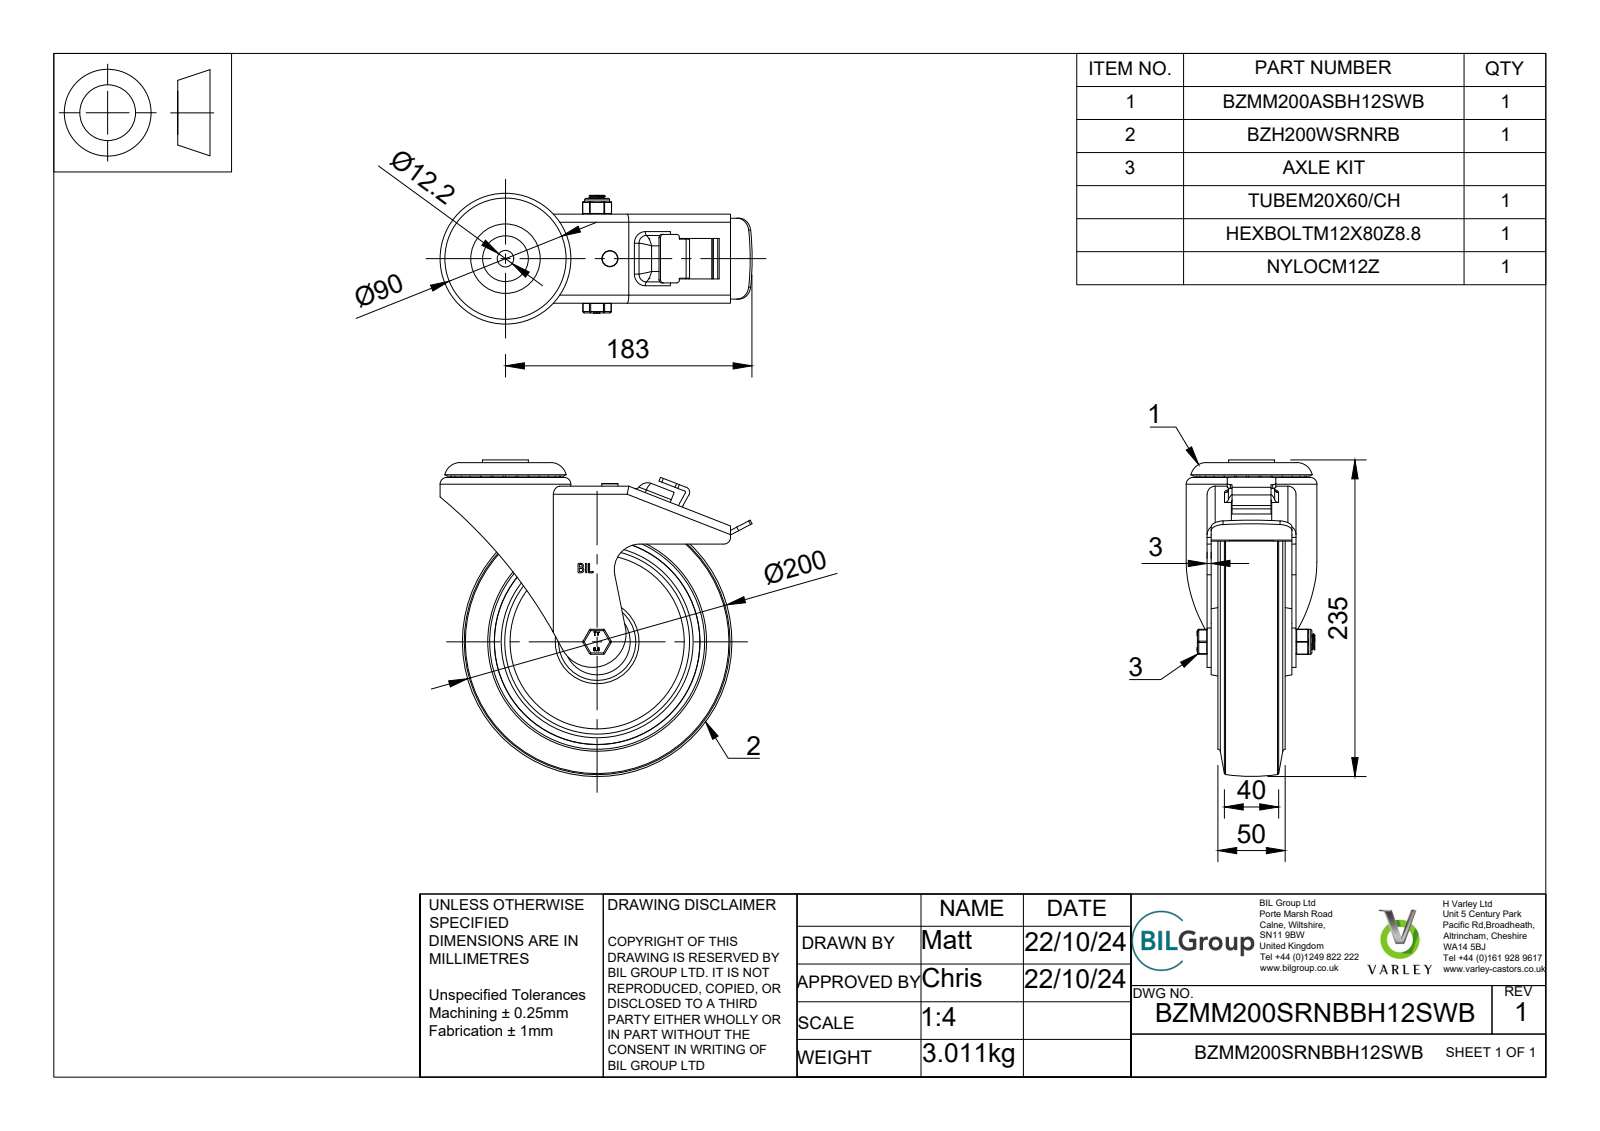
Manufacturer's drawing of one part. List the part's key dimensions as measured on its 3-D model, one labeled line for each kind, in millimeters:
Part name (STEP PRODUCT): BZMM200SRNBBH12SWB v3; BZMM200ASBH12SWB v1; ZINC PLATED, PRESSED STEEL HEAD; ZINC PLATED, PRESSED STEEL HEAD Geometry (+8 more)
STEP written by: Autodesk Translation Framework v13.20.0.188 (AUTOMOTIVE_DESIGN)
Units: millimetres
Bodies: 68 solids, 801 faces (375 planar, 254 cylindrical, 172 other)
Overall size (bounding box): 235 × 231.5 × 97
Volume: 1 195 000 mm³ · Surface area: 333 146 mm²
Round holes (diameter × count): ⌀6 ×1, ⌀7 ×1, ⌀10 ×1, ⌀12 ×1, ⌀12.2 ×1, ⌀12.3 ×1, ⌀12.5 ×1, ⌀14 ×1, ⌀20 ×1, ⌀30.2 ×1, ⌀51 ×1, ⌀58 ×1
Round bosses / shafts (diameter × count): ⌀5 ×8, ⌀97 ×1, ⌀78 ×1, ⌀39 ×1, ⌀34 ×1, ⌀30 ×1, ⌀24 ×1, ⌀19.9 ×1
Partial cylindrical surfaces — rounded edges, fillets, slot ends (radius × count): R1.5 ×30, R0.5 ×24, R1 ×13, R0.25 ×12, R0.75 ×10, R2 ×10, R3 ×6, R3.25 ×6
Main face-to-face distances: 3, 25, 35, 28, 38, 63, 5, 10, 20, 8
Hole centre spacings: 77.5
